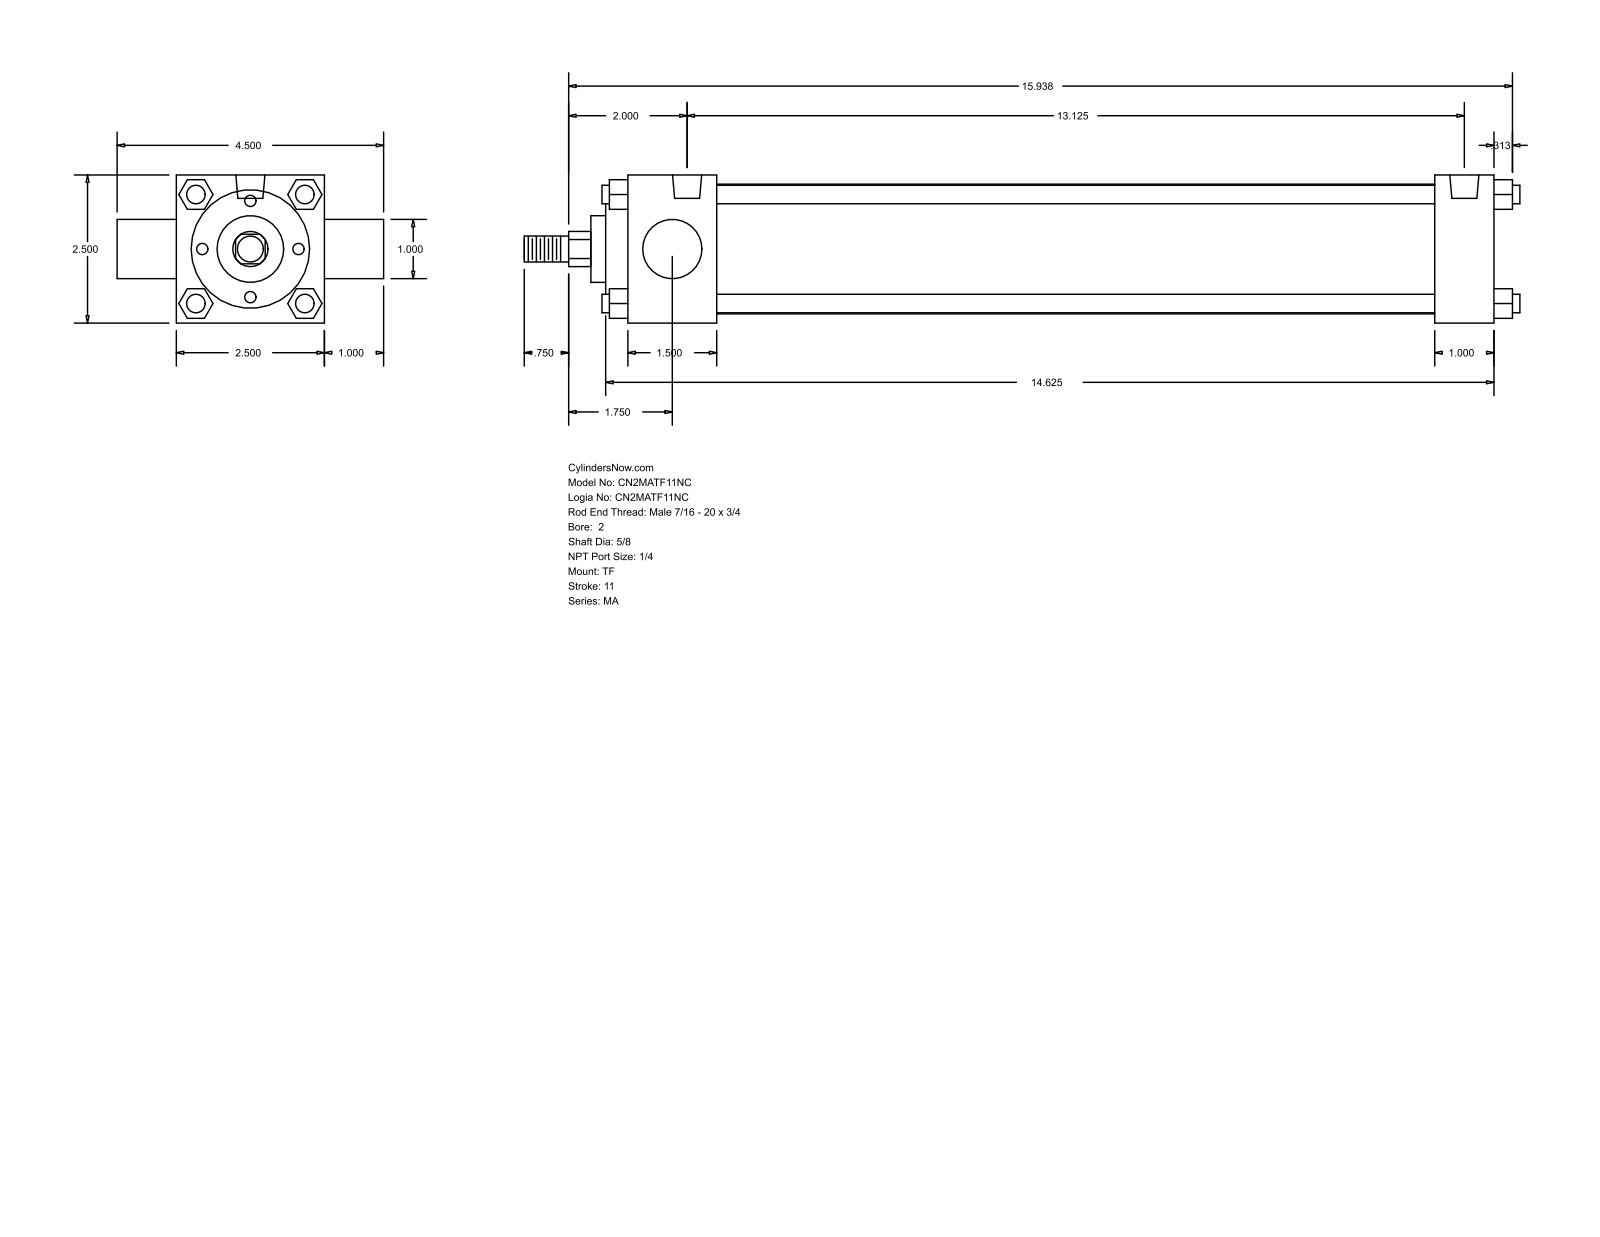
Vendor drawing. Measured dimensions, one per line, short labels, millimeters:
name: MA_TF__0200_0.625
written by: GSSL Pune (CONFIG_CONTROL_DESIGN)
unit: mm
bodies: 0 solids, 122 faces (93 planar, 29 cylindrical, 0 other)
size: 427.04 × 114.3 × 63.5
holes: 3× ⌀7.94, 2× ⌀12.49
bosses: 4× ⌀7.94, 1× ⌀55.63, 1× ⌀50.8, 1× ⌀28.57, 1× ⌀25.4, 1× ⌀15.88, 1× ⌀11.11
rounds: 1× R7.54
face distances: 63.5, 25.4, 38.1, 371.48, 12.7, 346.08, 307.98, 333.38, 9.52, 47.62
hole spacings: 333.38
